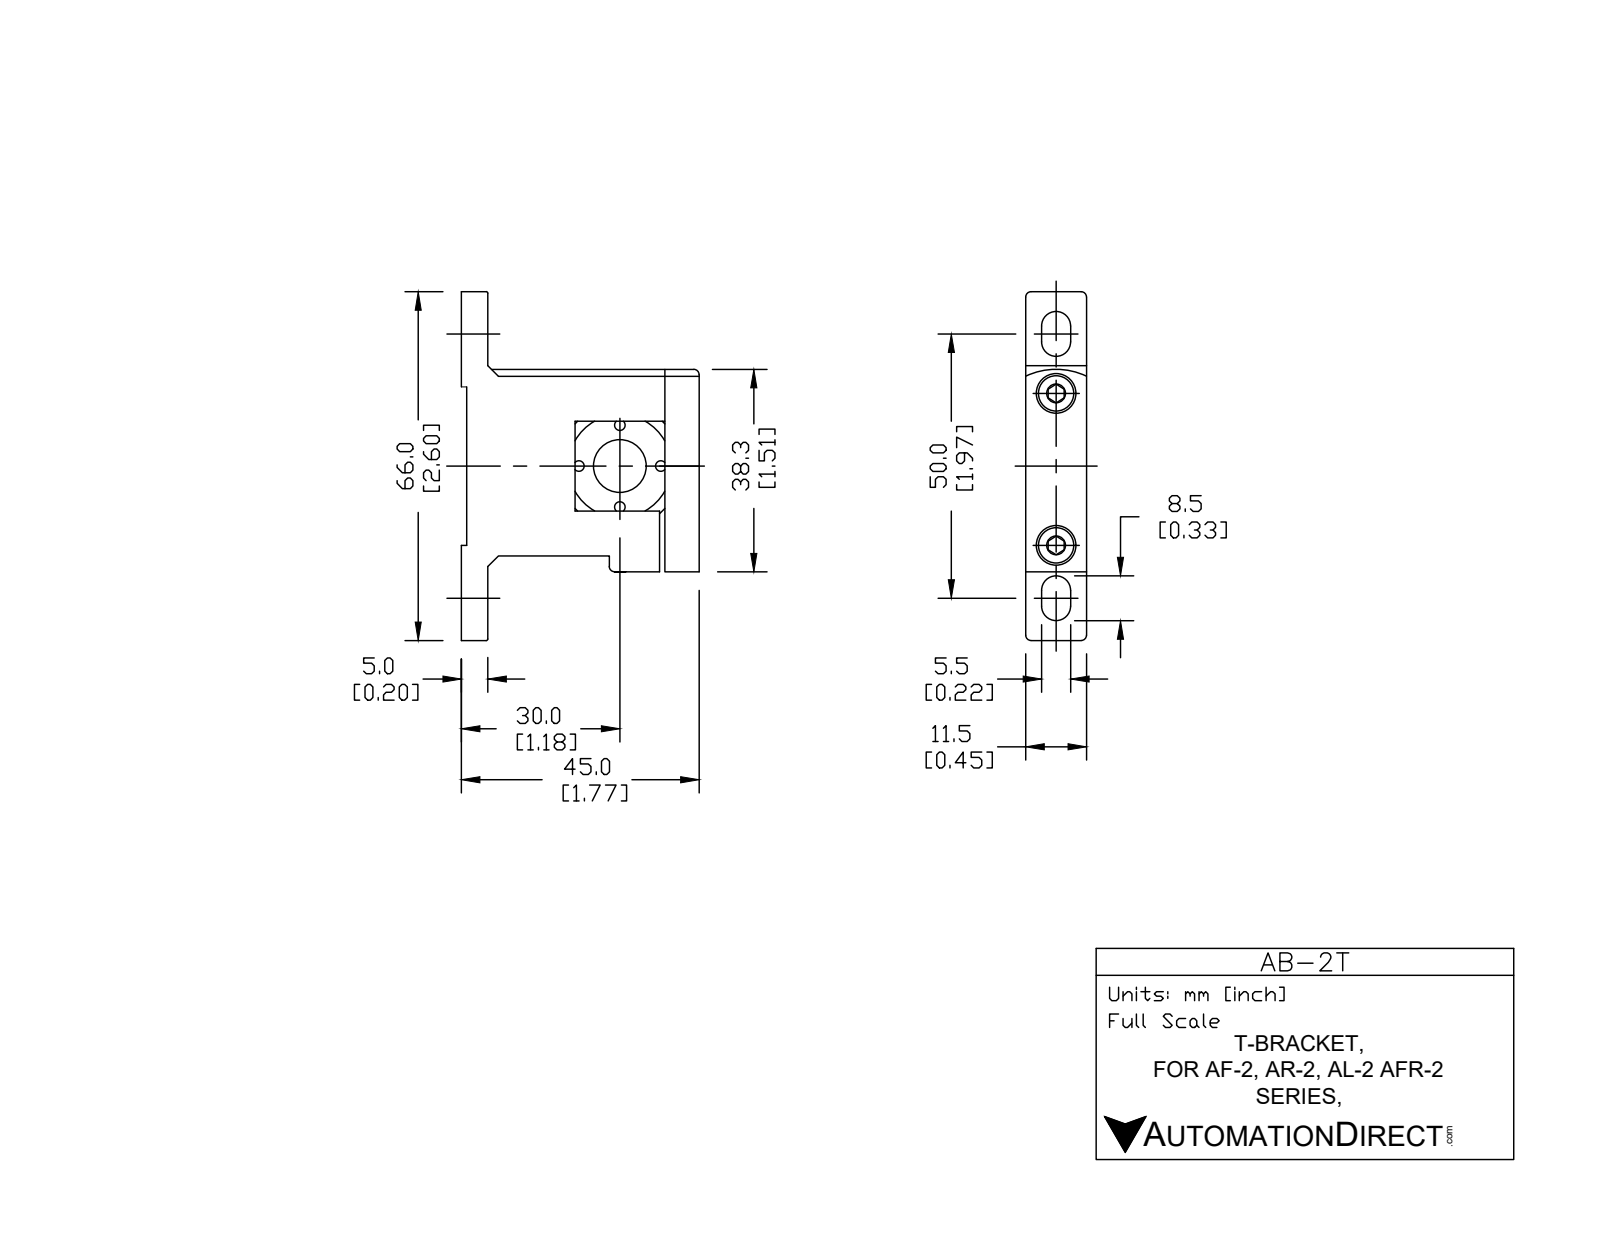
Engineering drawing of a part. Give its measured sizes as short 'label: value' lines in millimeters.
name: AB-2T
written by: SolidWorks 2015 (CONFIG_CONTROL_DESIGN)
unit: mm
bodies: 3 solids, 104 faces (68 planar, 24 cylindrical, 12 other)
size: 66 × 45 × 11.5
volume: 16 046 mm³; area: 8 100 mm²
holes: 2× ⌀4.5, 2× ⌀6.21, 1× ⌀10
bosses: 2× ⌀5.75, 2× ⌀4
rounds: 4× R2.75, 1× R1.5, 1× R13.37
face distances: 11.5, 20, 5, 1.5, 43.75, 40, 1.25, 18.5, 45, 3
hole spacings: 28.75
